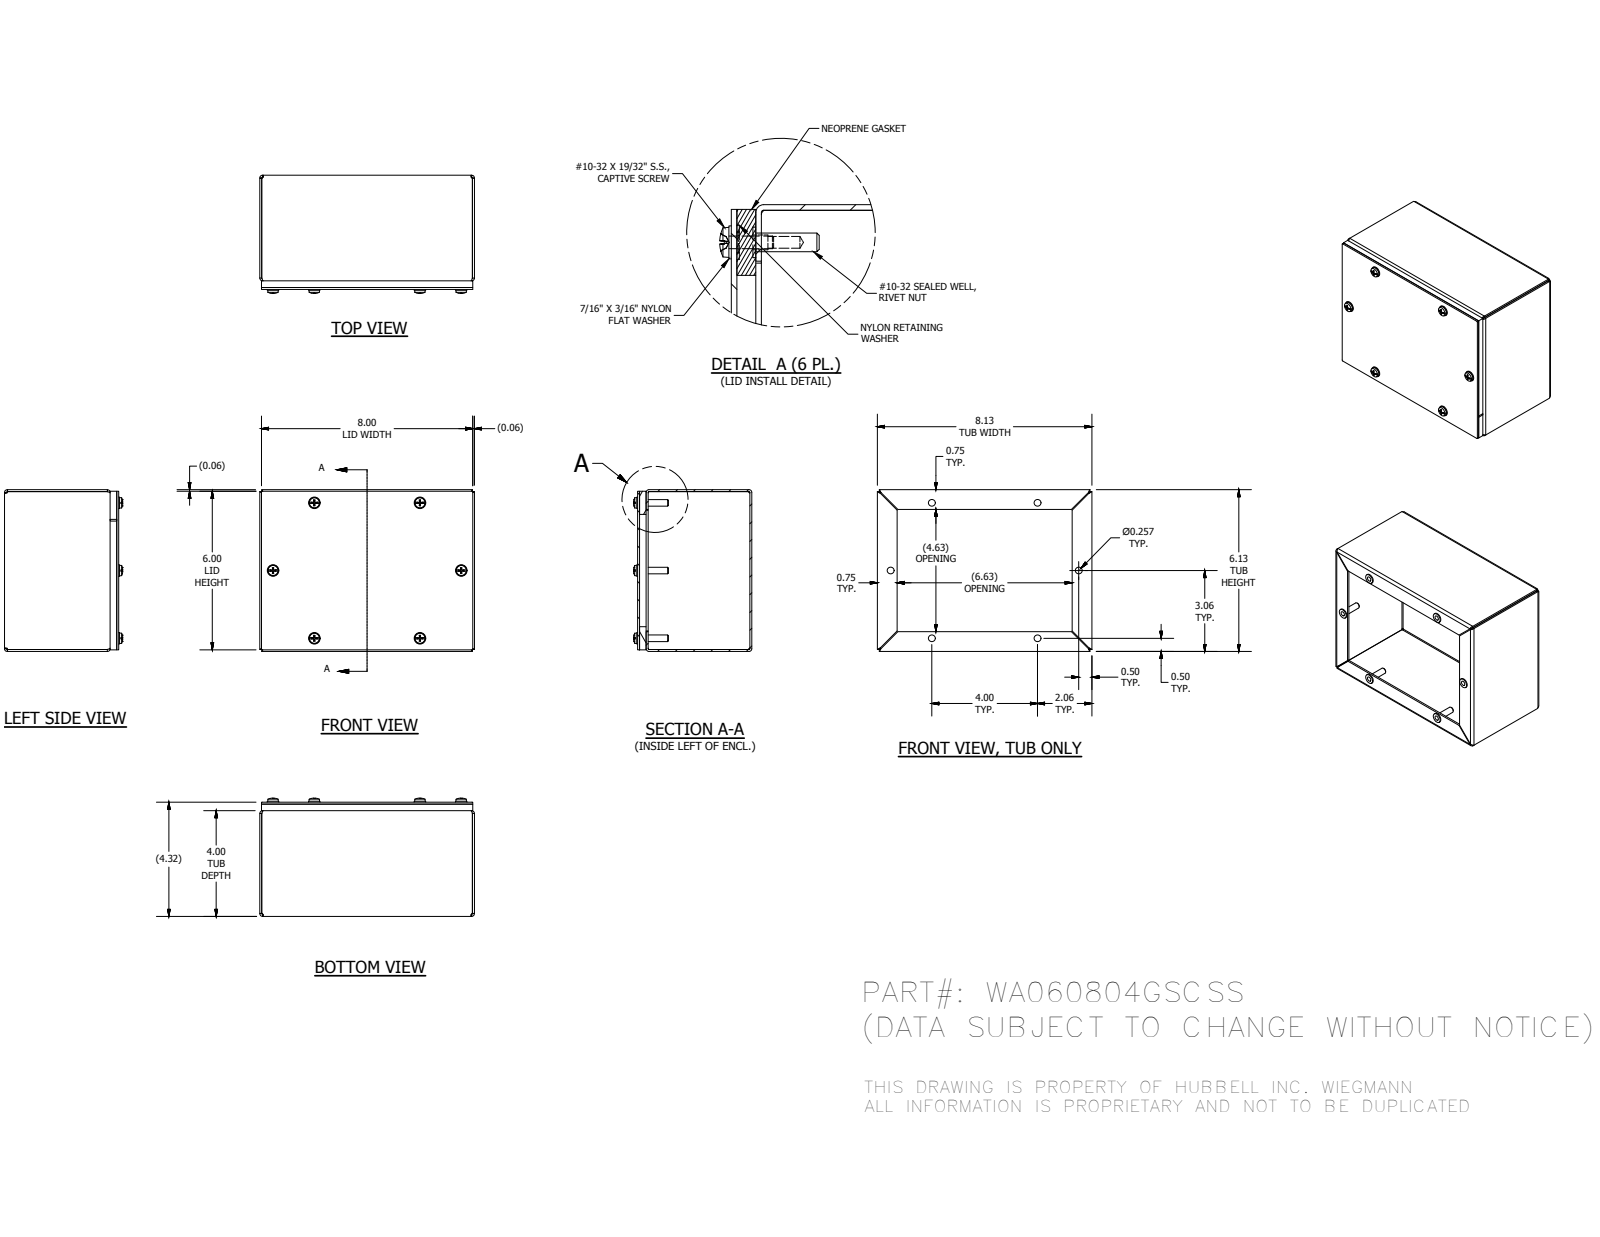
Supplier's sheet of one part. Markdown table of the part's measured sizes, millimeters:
| quantity | value |
| --- | --- |
| part name | WA060804GSCSSBKP; WA0608GSCSSLID; 316295; 37210 (+4 more) |
| STEP written by | Autodesk Inventor 2016 (AUTOMOTIVE_DESIGN) |
| units | millimeters |
| bodies | 28 solids, 602 faces (332 planar, 128 cylindrical, 142 other) |
| overall size | 206.38 × 155.57 × 113.75 |
| volume | 361 475 mm³ |
| surface area | 338 052 mm² |
| round holes (diameter × count) | 3.96 × 6, 4.78 × 6, 4.98 × 6, 6.53 × 6, 7.06 × 6, 7.14 × 6, 7.95 × 6 |
| round bosses / shafts (diameter × count) | 11.51 × 6, 11.11 × 6, 10.31 × 6, 6.3 × 6, 4.25 × 6 |
| partial cylindrical surfaces (radius × count) | 0.79 × 12, 1.78 × 8, 2.67 × 8, 2.27 × 6 |
| main face-to-face distances | 1.88, 107.95, 153.7, 99.72, 8.23, 106.07, 109.83, 204.5, 6.35, 101.6 |
| hole center spacings | 101.6, 155.54, 76.21, 76.22, 76.23, 76.24, 130.16, 155.55 |
